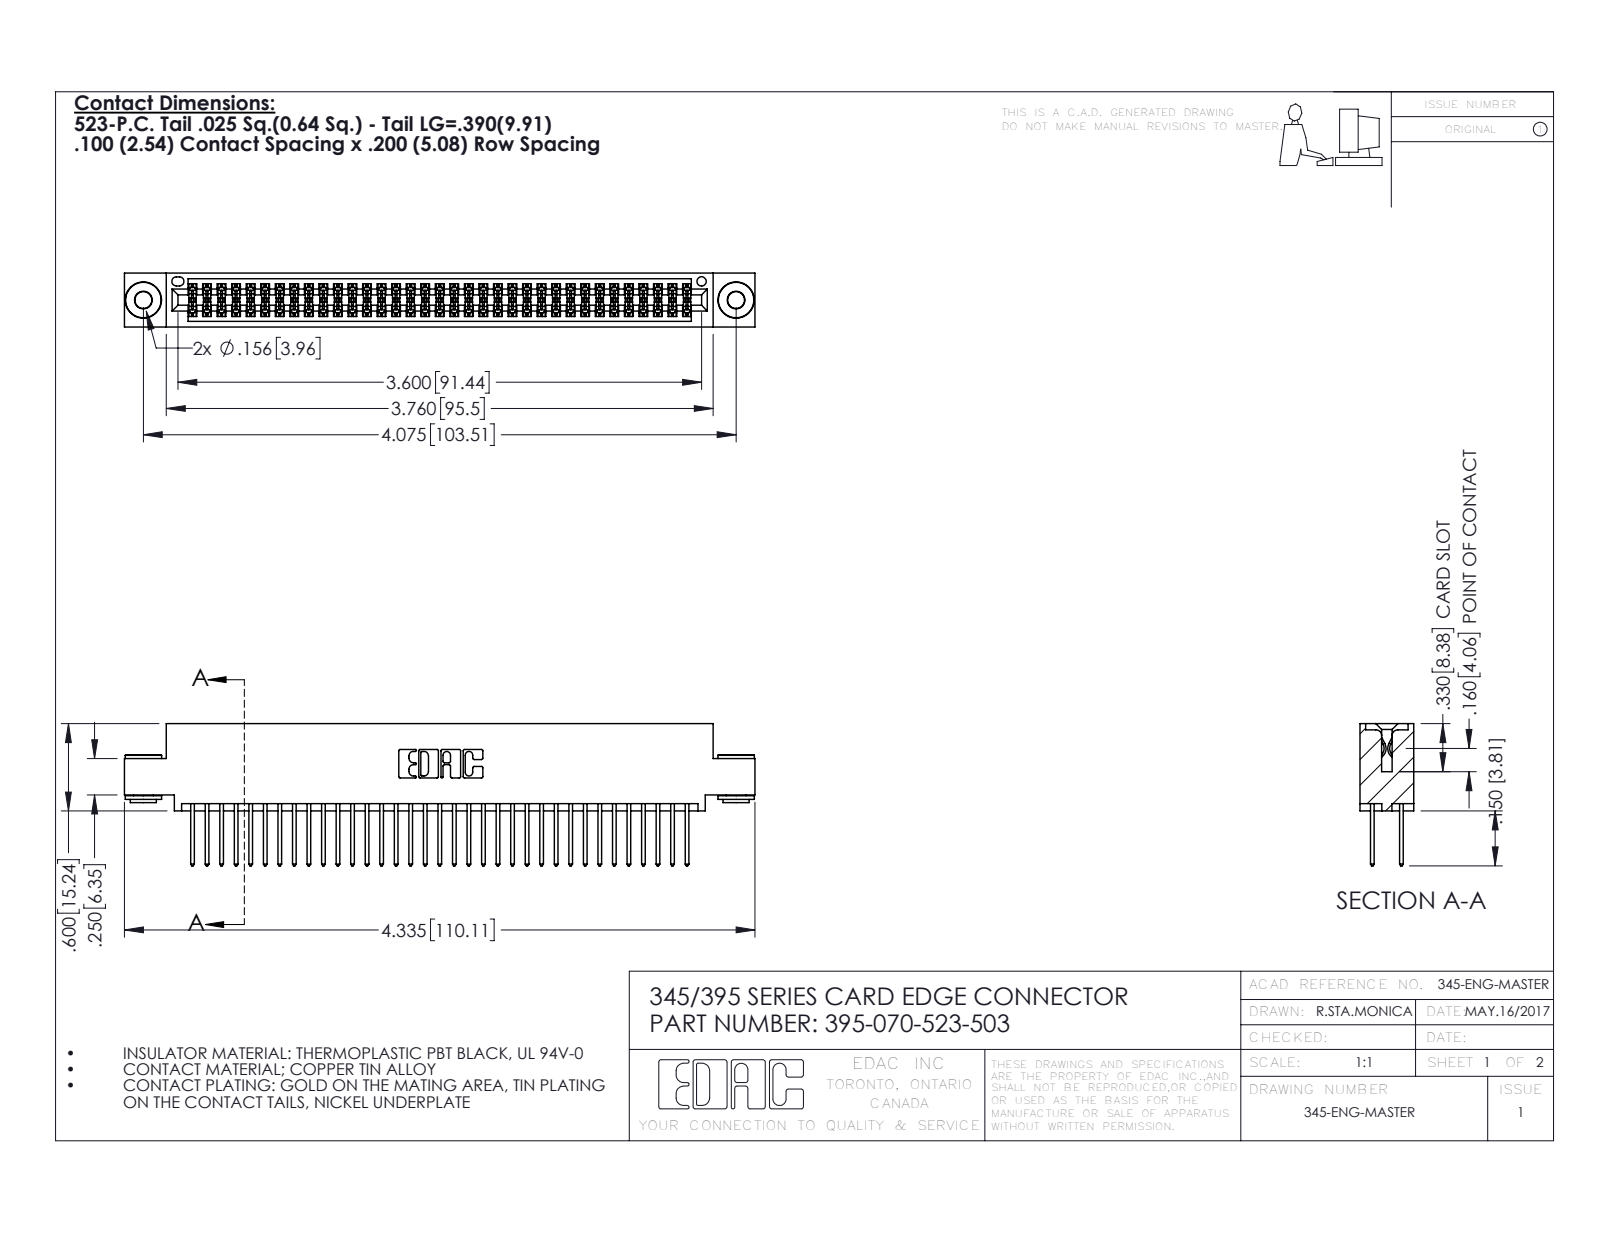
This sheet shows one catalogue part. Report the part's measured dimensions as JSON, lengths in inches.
{"part_name": "345-250-002_345-250-002-102; 395-070-523-503; 345-292-001_345-293-123; 345 Part_0.110 Offset - 0.156 Dia-TH", "step_written_by": "SolidWorks 2016 (CONFIG_CONTROL_DESIGN)", "units": "inches", "bodies": {"solids": 73, "faces": 3668, "planar": 2404, "cylindrical": 1256, "other": 8}, "overall_size": [4.335, 0.977, 0.37], "volume_in3": 0.654, "surface_area_in2": 25.81, "round_holes": [[0.116, 2], [0.156, 2], [0.064, 1]], "round_bosses_or_shafts": [[0.25, 2], [0.18, 2], [0.136, 2]], "partial_cylinders_radius": [[0.006, 105], [0.01, 70], [0.01, 22], [0.007, 6], [0.031, 6], [0.026, 3], [0.014, 2], [0.019, 2]], "face_to_face_distances": [0.072, 0.298, 0.2, 0.025, 0.098, 0.272, 0.37, 0.225, 0.175, 0.149], "hole_center_spacings": [0.27, 3.839, 4.075]}
